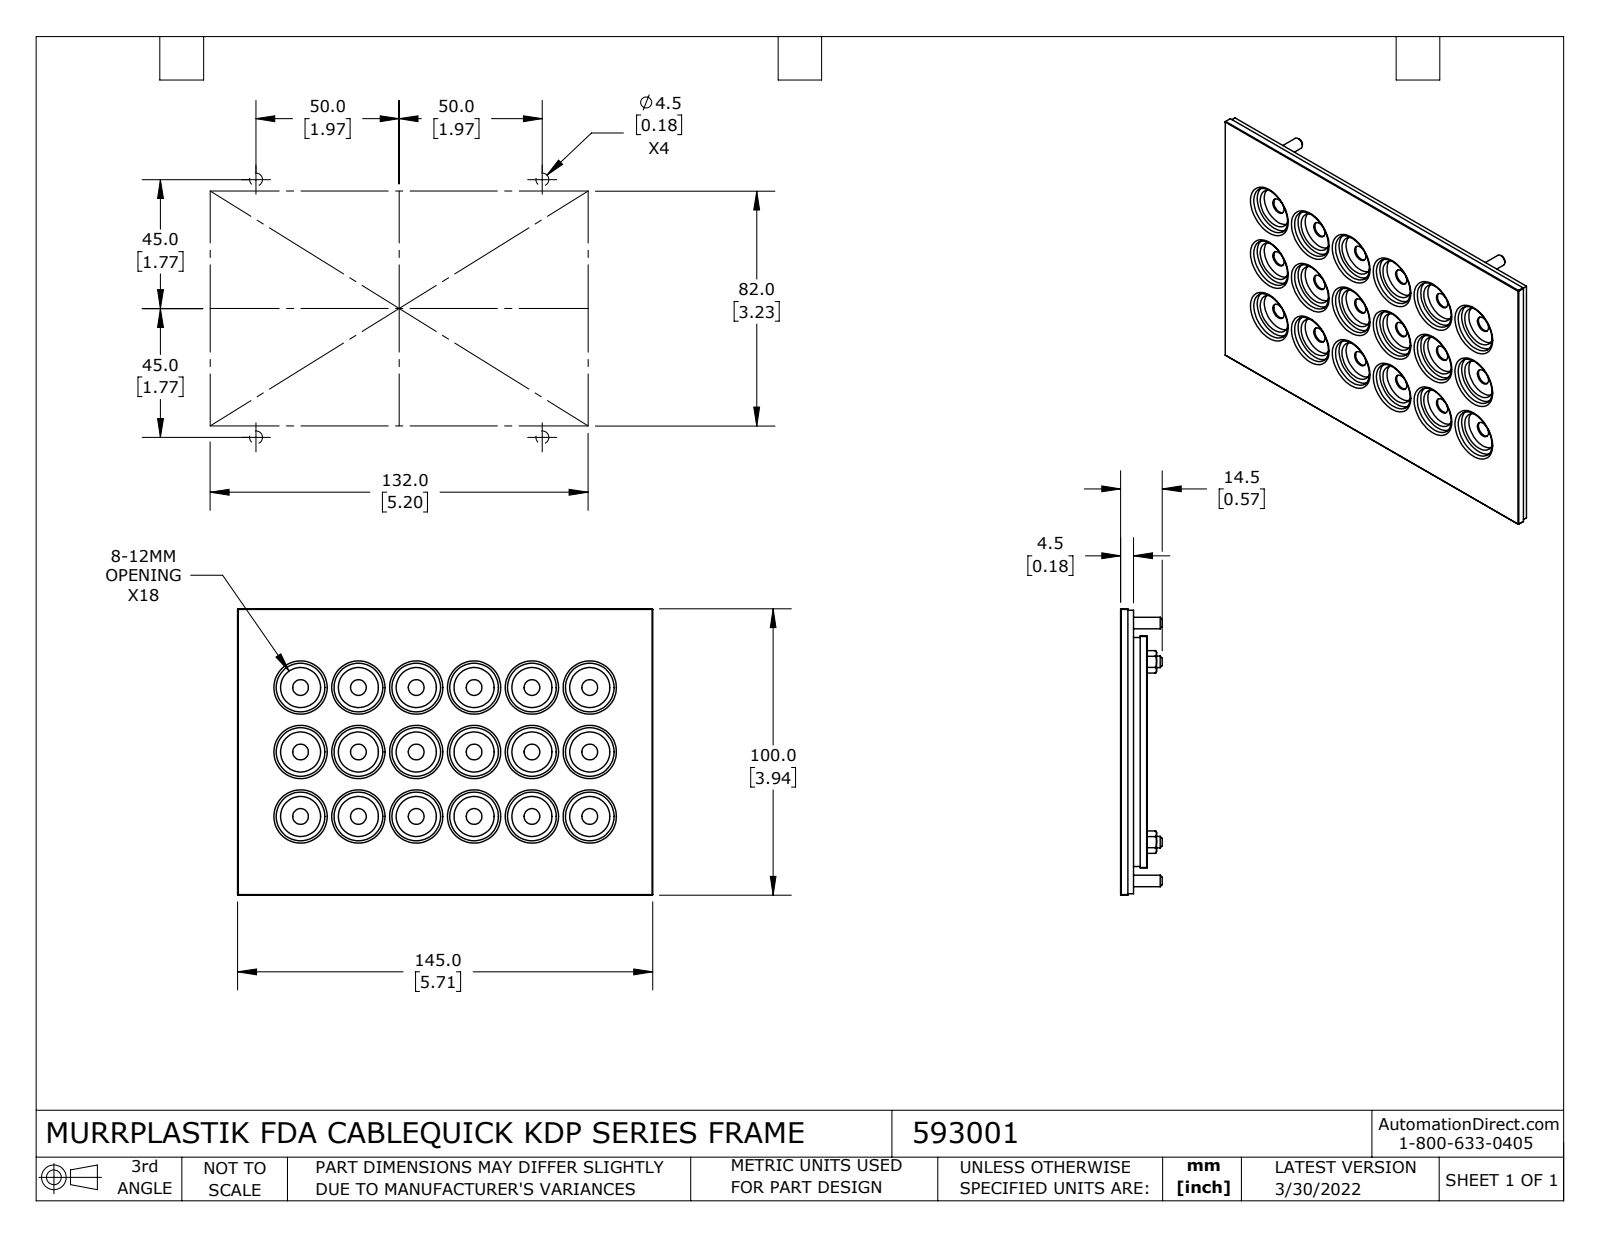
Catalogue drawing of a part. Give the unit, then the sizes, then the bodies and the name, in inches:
Units: inches
Overall size (bounding box): 5.709 × 3.937 × 0.571
Round holes (diameter × count): ⌀0.217 ×26, ⌀0.551 ×18, ⌀0.669 ×18, ⌀0.709 ×18, ⌀0.177 ×4
Round bosses / shafts (diameter × count): ⌀0.157 ×8
Partial cylindrical surfaces — rounded edges, fillets, slot ends (radius × count): R0.236 ×4, R0.256 ×4
Main face-to-face distances: 0.098, 0.268, 0.177, 0.189, 0.366, 0.091, 0.02, 0.169, 0.079, 0.374
Hole centre spacings: 1.191, 1.82, 0.795, 0.886, 1.591, 2.545, 1.772, 1.942
Volume: 5.38 in³ · Surface area: 64.21 in²
Bodies: 1 solid, 510 faces (181 planar, 203 cylindrical, 126 other)
Part name (STEP PRODUCT): 593001
STEP written by: SolidWorks 2021 (CONFIG_CONTROL_DESIGN)
